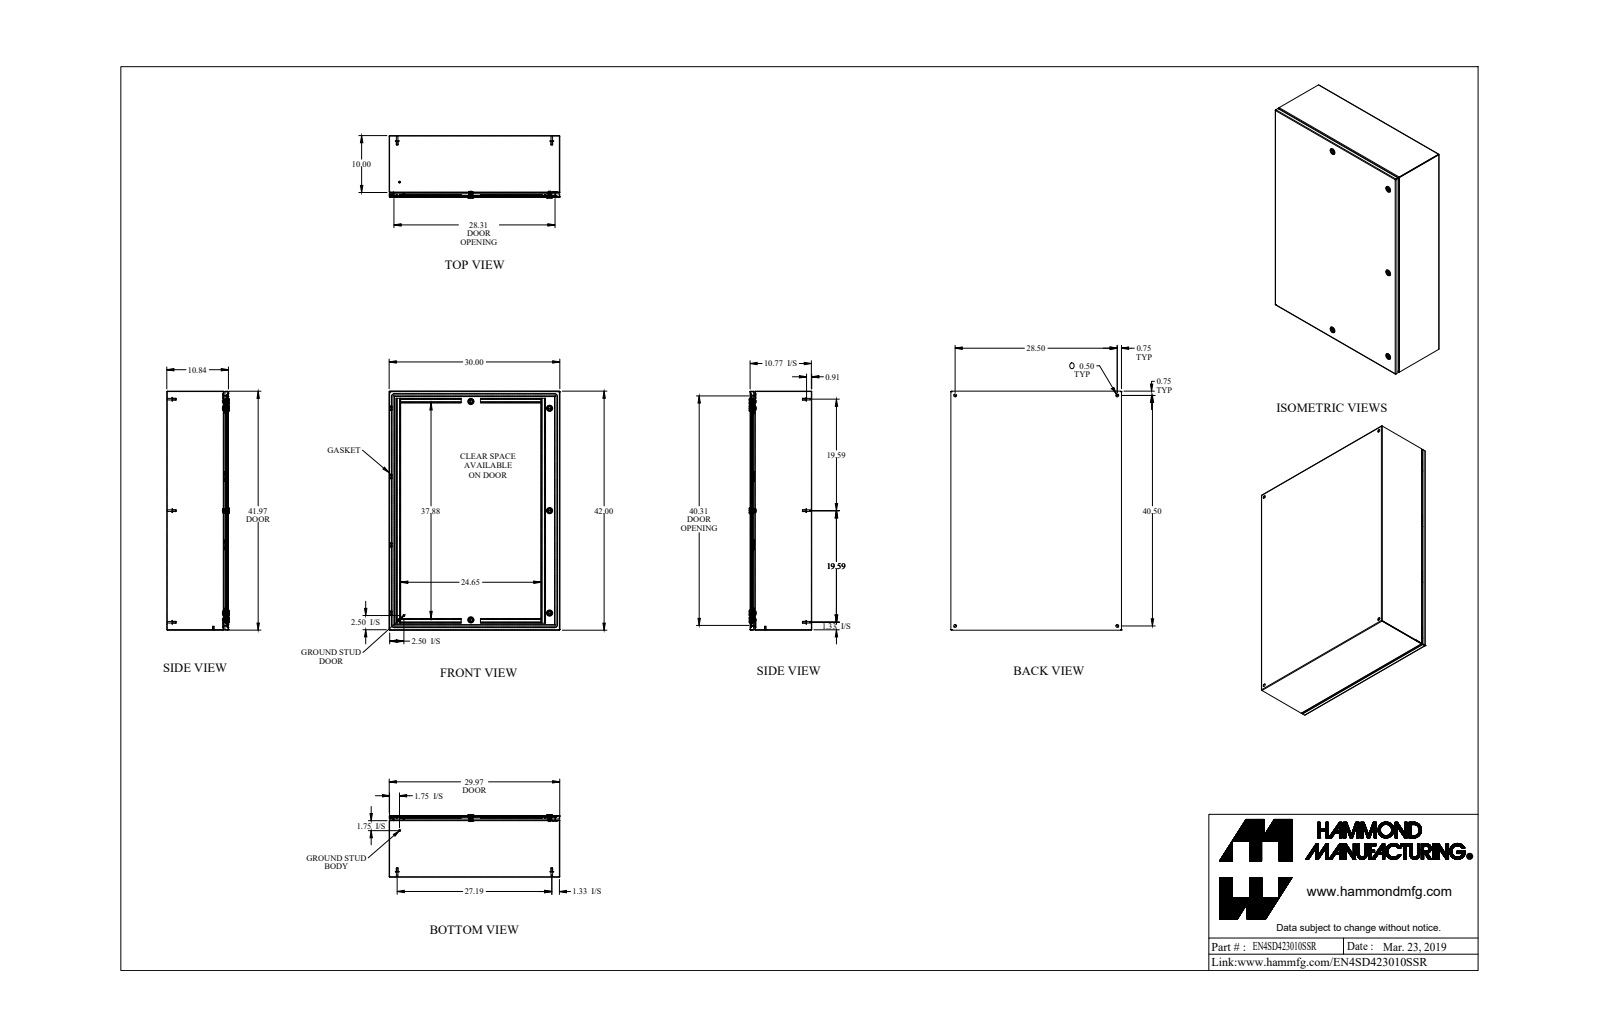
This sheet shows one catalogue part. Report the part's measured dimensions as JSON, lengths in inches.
{"part_name": "EN4SD423010SSR", "step_written_by": "SolidWorks 2019 (AUTOMOTIVE_DESIGN)", "units": "inches", "bodies": {"solids": 58, "faces": 1511, "planar": 807, "cylindrical": 474, "other": 230}, "overall_size": [42, 30, 11.002], "volume_in3": 331.4, "surface_area_in2": 9357, "round_holes": [[0.5, 9], [0.197, 5], [0.387, 5], [0.63, 5], [0.768, 5], [0.172, 1], [0.24, 1], [0.242, 1]], "round_bosses_or_shafts": [[0.625, 10], [0.313, 8], [0.275, 6], [1.1, 5], [0.236, 5], [0.525, 4], [0.785, 3], [0.785, 2]], "partial_cylinders_radius": [[0.01, 24], [0.048, 24], [0.036, 20], [0.108, 20], [0.125, 10], [0.006, 8], [0.04, 8], [0.062, 8]], "face_to_face_distances": [0.072, 10.77, 10.698, 10.842, 29.928, 41.928, 29.856, 30, 41.856, 42], "hole_center_spacings": [2.502, 13.642, 13.891, 14.937, 17.985, 20.278, 23.658, 27.532]}
